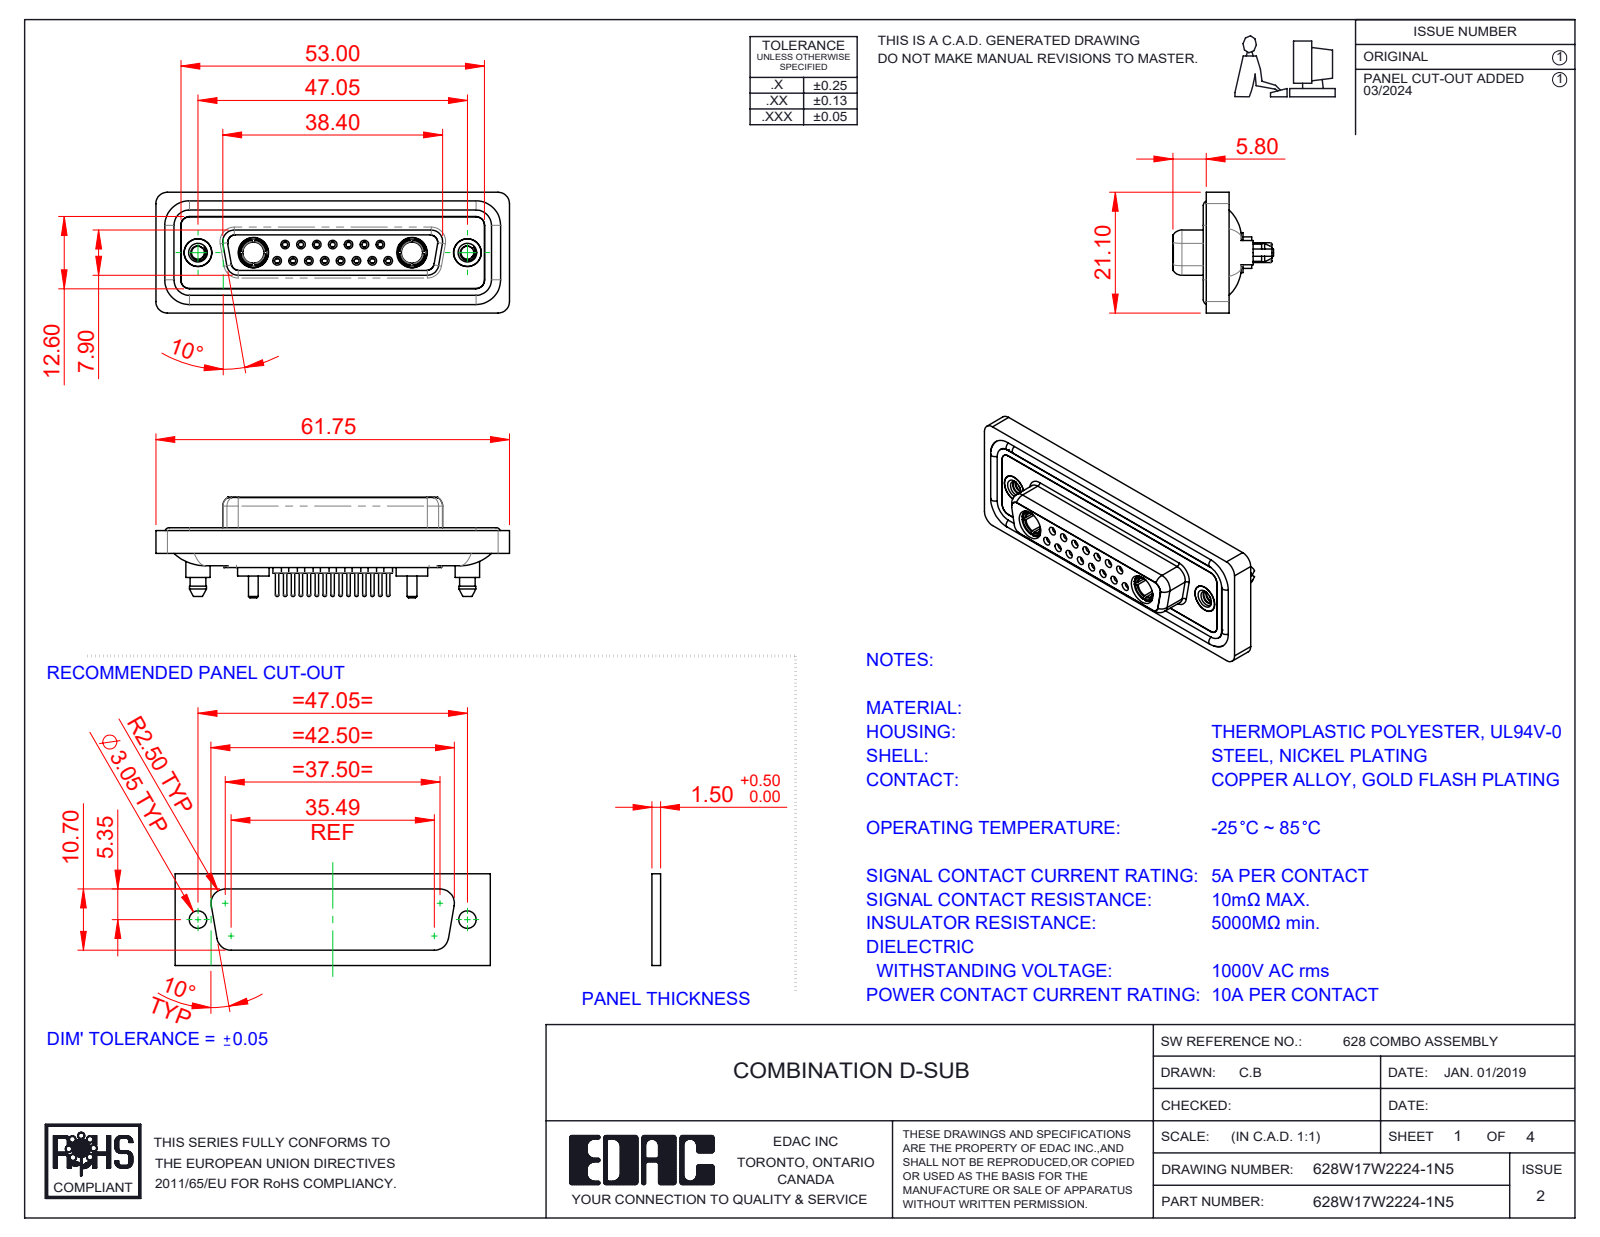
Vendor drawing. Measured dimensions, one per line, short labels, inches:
name: 628Combo Contact Row 1_24; 628Combo Housing_17W2; 628Combo Shell Front_25 Contacts; Power Socket_10A S (+5 more)
written by: SolidWorks 2023 (CONFIG_CONTROL_DESIGN)
unit: in
bodies: 26 solids, 1409 faces (404 planar, 551 cylindrical, 454 other)
size: 2.431 × 0.831 × 0.691
volume: 0.514 in³; area: 21.95 in²
holes: 15× ⌀0.035, 15× ⌀0.043, 15× ⌀0.059, 15× ⌀0.079, 8× ⌀0.063, 7× ⌀0.067, 4× ⌀0.191, 2× ⌀0.089, 2× ⌀0.146, 2× ⌀0.157, 2× ⌀0.159, 2× ⌀0.197
bosses: 15× ⌀0.087, 15× ⌀0.024, 11× ⌀0.063, 2× ⌀0.217, 2× ⌀0.213, 2× ⌀0.205, 2× ⌀0.195, 2× ⌀0.195
rounds: 24× R0.059, 18× R0.079, 10× R0.063, 8× R0.053, 4× R0.01, 4× R0.02, 4× R0.024, 4× R0.026
face distances: 0.016, 0.071, 0.293, 0.222, 0.26, 0.02, 0.278, 0.063, 0.114, 0.043
hole spacings: 0.124, 0.109, 0.327, 0.218, 0.198, 0.198, 0.295, 0.436
